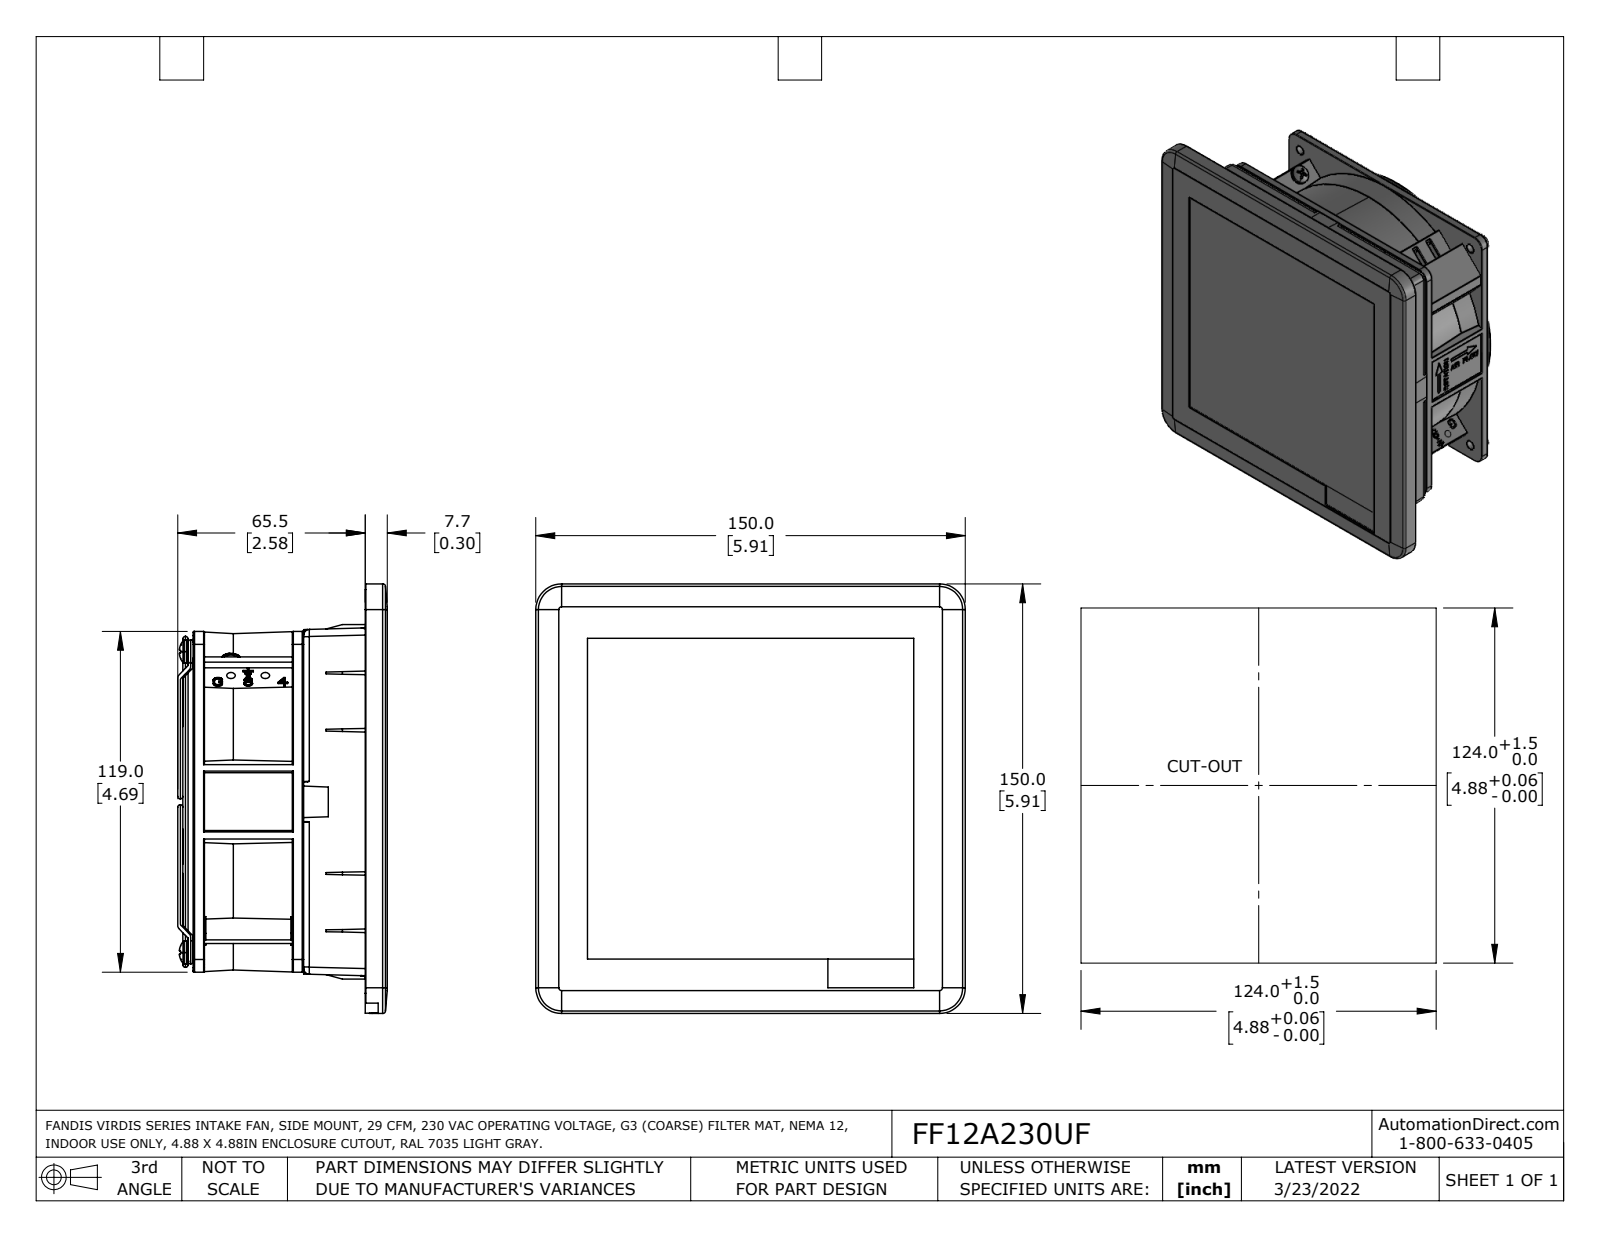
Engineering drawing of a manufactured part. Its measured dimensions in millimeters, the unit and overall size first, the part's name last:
Units: millimetres
Overall size (bounding box): 150 × 150 × 73.2
Round holes (diameter × count): ⌀4.3 ×4, ⌀1 ×1
Round bosses / shafts (diameter × count): ⌀8 ×5
Partial cylindrical surfaces — rounded edges, fillets, slot ends (radius × count): R0.3 ×13, R0.3 ×7, R4.5 ×5, R1 ×4, R1.5 ×4, R7 ×4, R9 ×4, R0.2 ×2
Main face-to-face distances: 67.3, 0.5, 67.8, 7.7, 7.2, 60.1, 33.1, 63.3, 4, 32.6
Hole centre spacings: 104.8, 148.2, 14, 90.9, 107.4, 140.1
Volume: 937 500 mm³ · Surface area: 103 900 mm²
Bodies: 17 solids, 1232 faces (946 planar, 105 cylindrical, 181 other)
Part name (STEP PRODUCT): FF12A230UF
STEP written by: SolidWorks 2021 (AUTOMOTIVE_DESIGN)
